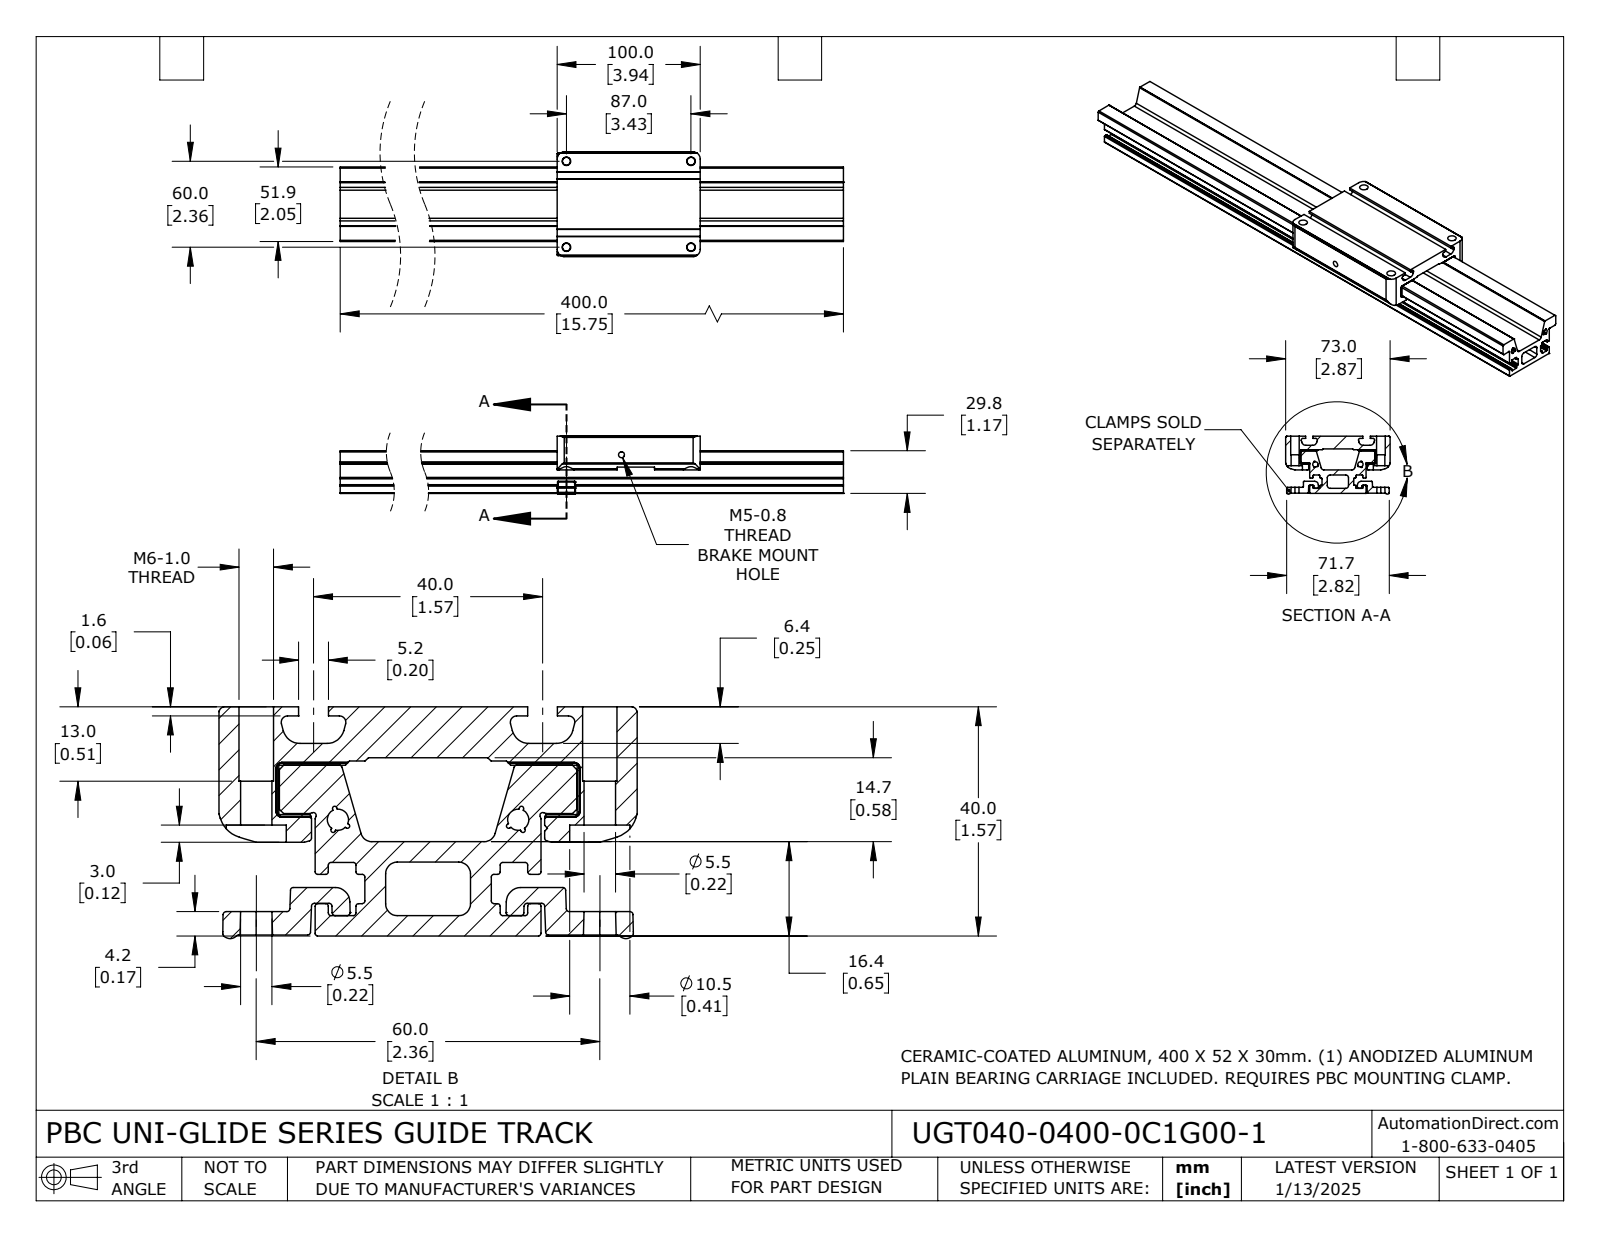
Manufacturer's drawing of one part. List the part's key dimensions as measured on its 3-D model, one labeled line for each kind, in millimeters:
Part name (STEP PRODUCT): UGT040-0400-0C1G00-1_RAIL; UGT040-0400-0C1G00-1_CARRIAGE; UGT040-0400-0C1G00-1
STEP written by: SolidWorks 2023 (CONFIG_CONTROL_DESIGN)
Units: millimetres
Bodies: 10 solids, 445 faces (248 planar, 178 cylindrical, 19 other)
Overall size (bounding box): 400 × 73 × 40
Volume: 339 500 mm³ · Surface area: 167 000 mm²
Round holes (diameter × count): ⌀2.5 ×4, ⌀3 ×4, ⌀5.5 ×4, ⌀6 ×4, ⌀10.5 ×4, ⌀3.7 ×2, ⌀4.2 ×1
Partial cylindrical surfaces — rounded edges, fillets, slot ends (radius × count): R0.5 ×26, R1 ×8, R2.4 ×8, R0.4 ×6, R5 ×6, R0.5 ×4, R0.9 ×4, R1.1 ×4
Main face-to-face distances: 3.6, 12.9, 29.8, 16.5, 13.4, 26.2, 23.5, 40, 36.4, 10.2
Hole centre spacings: 15, 31, 41, 46, 56, 58, 59.9, 60
